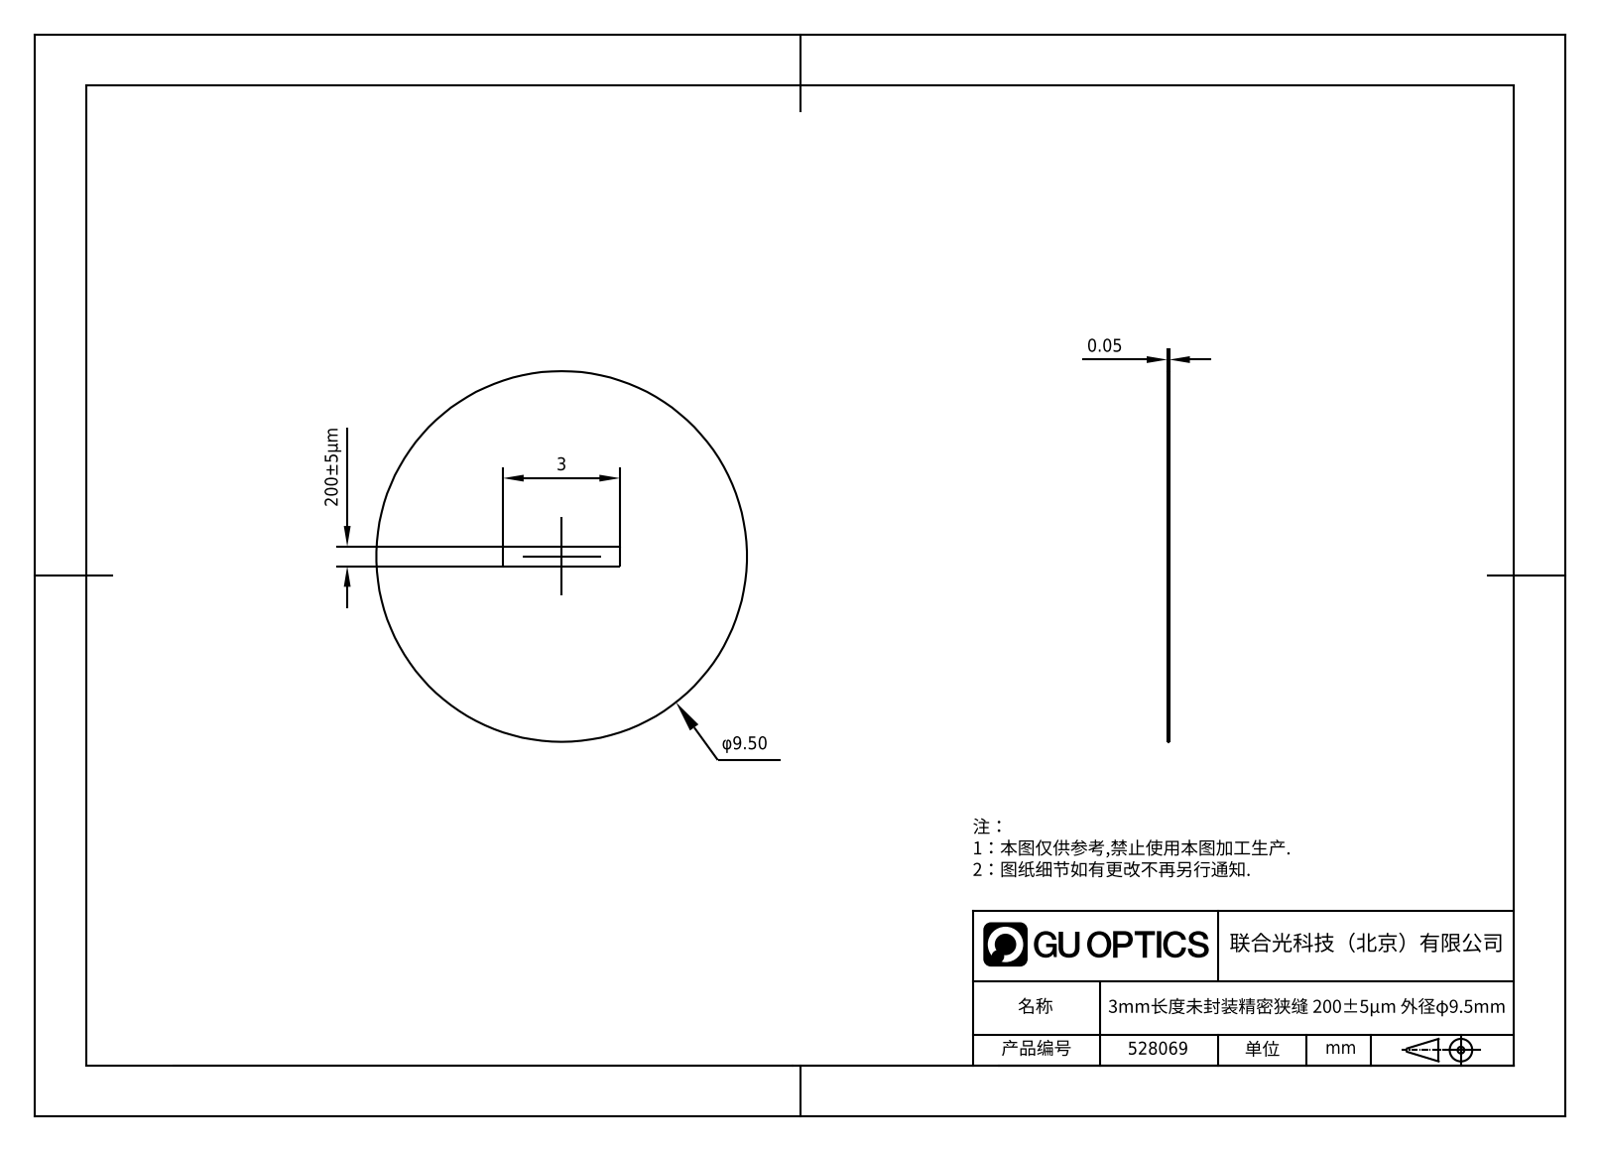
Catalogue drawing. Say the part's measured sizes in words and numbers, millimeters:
The part is named "1.5.4.10-ZXG-9.5-200". Its 3-D file was written by "SolidWorks 2021 (CONFIG_CONTROL_DESIGN)". It is 1 solid with 8 faces: 6 planar, 2 cylindrical and 0 other. Overall it measures 9.5 by 9.5 by 0.05 millimeters. Its volume is 4 cubic millimeters and its surface area 142 square millimeters. Round bosses or shafts: 1 of diameter 9.5. The main face-to-face distances are 3.
